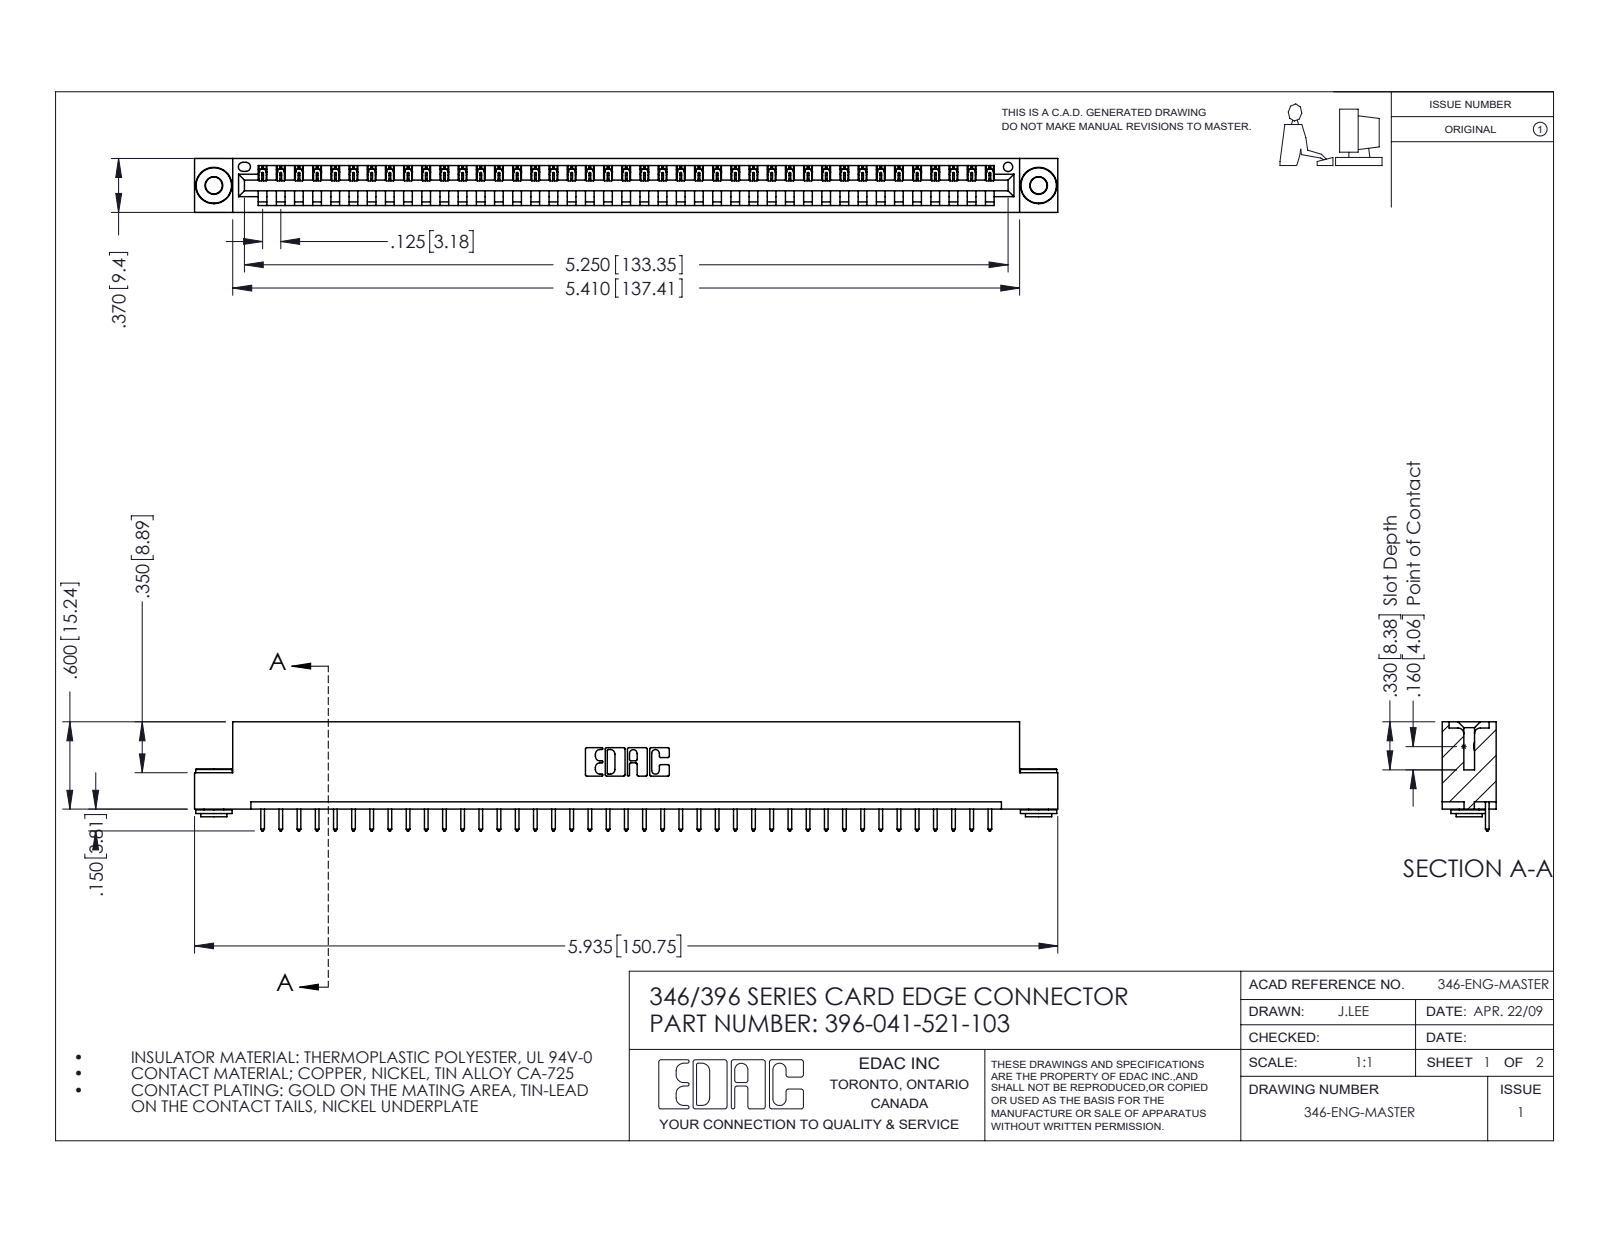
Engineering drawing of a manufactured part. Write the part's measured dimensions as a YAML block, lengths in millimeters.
part_name: "345-292-001_345-293-121; 346 Part_Flush Mounting Lugs - 0.156 Dia-TH; 396-041-521-103; 345-250-002_345-250-002-102"
step_written_by: "SolidWorks 2016 (CONFIG_CONTROL_DESIGN)"
units: millimeters
bodies: {solids: 44, faces: 2538, planar: 1726, cylindrical: 804, other: 8}
overall_size: [150.7, 19.1, 9.4]
volume: 14300
surface_area: 17650
round_holes:
  - {diameter: 2.9, count: 2}
  - {diameter: 4, count: 2}
  - {diameter: 1.6, count: 1}
round_bosses_or_shafts:
  - {diameter: 6.4, count: 2}
  - {diameter: 4.6, count: 2}
  - {diameter: 3.5, count: 2}
partial_cylinders:
  - {radius: 0.2, count: 82}
  - {radius: 0.3, count: 82}
  - {radius: 0.3, count: 22}
  - {radius: 0.2, count: 6}
  - {radius: 0.8, count: 6}
  - {radius: 0.7, count: 3}
  - {radius: 0.8, count: 2}
  - {radius: 1, count: 2}
face_to_face_distances: [1.2, 8.2, 9.4, 6.4, 0.6, 1.8, 7.6, 3.8, 5.6, 2.5]
hole_center_spacings: [6.2, 138.7, 144]
